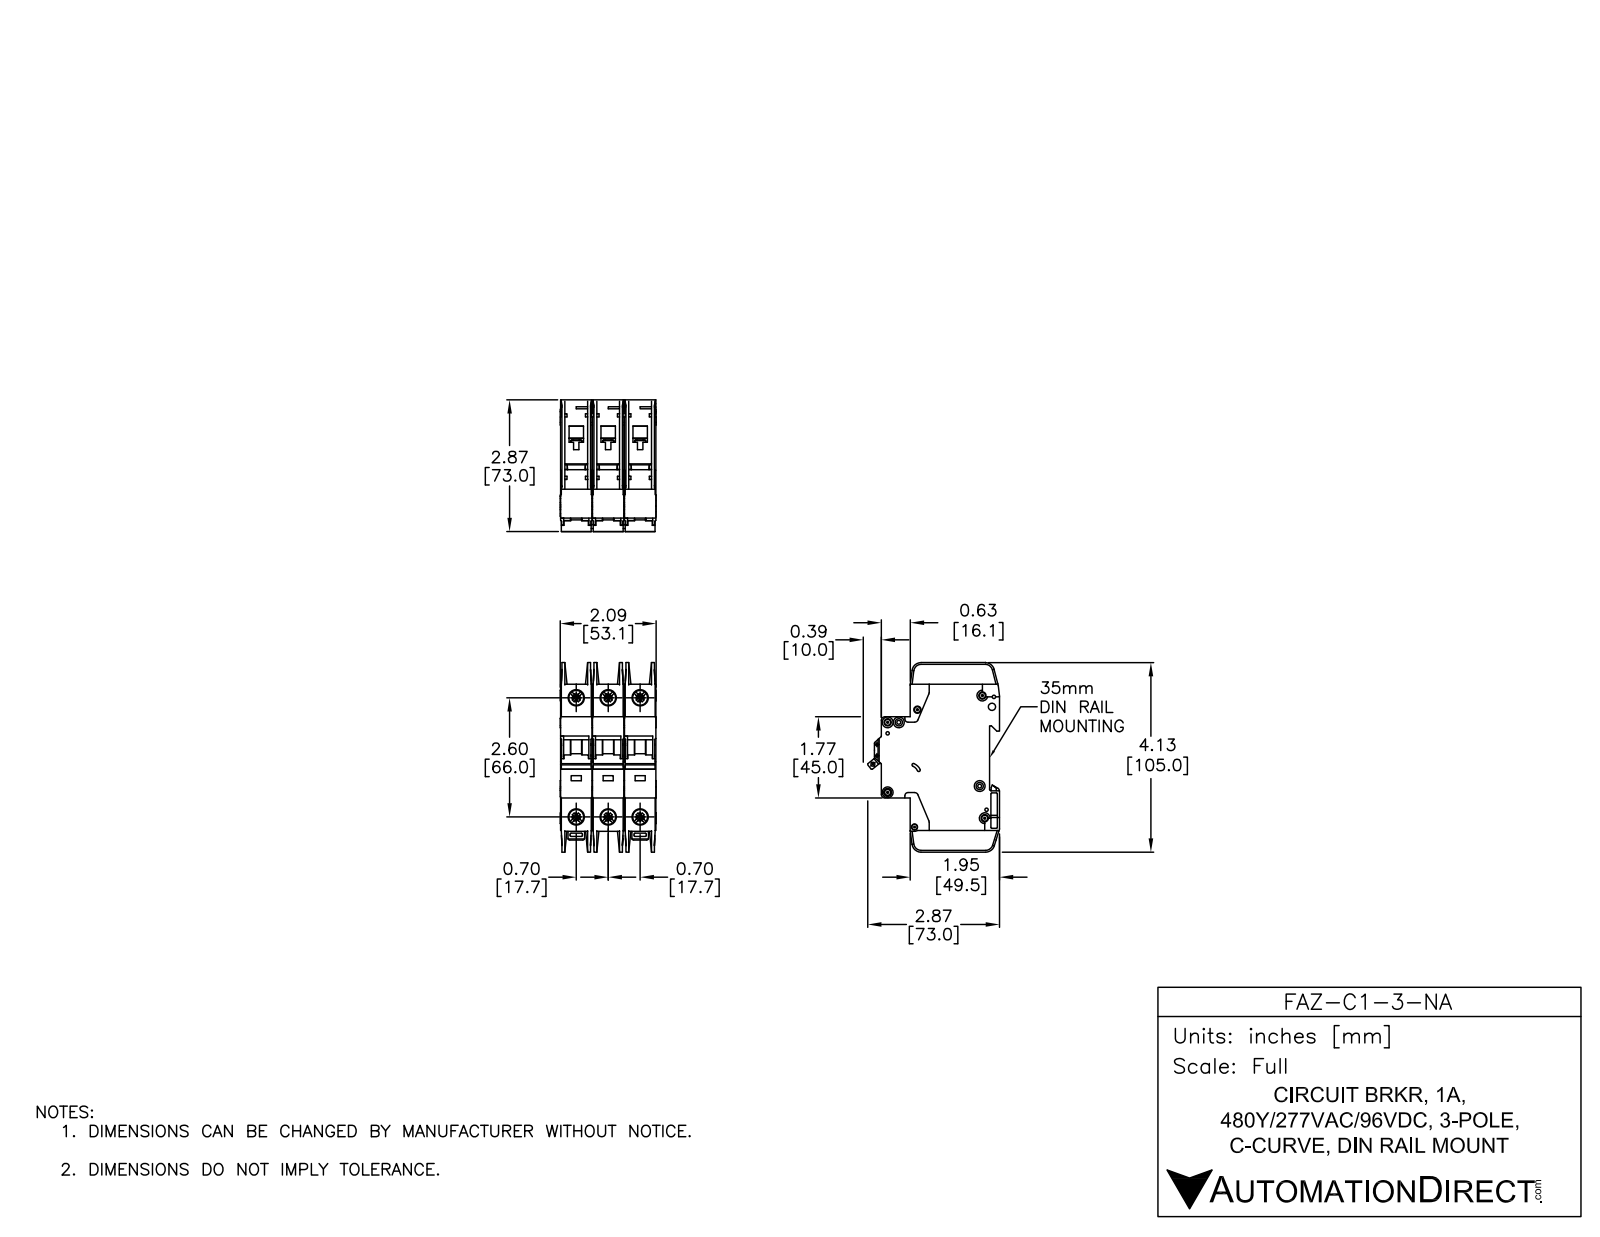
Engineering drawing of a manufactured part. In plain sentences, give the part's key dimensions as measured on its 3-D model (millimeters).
The part is named "FAZ-C1-3-NA". Its 3-D file was written by "SolidWorks 2014 (AUTOMOTIVE_DESIGN)". It is 9 solids with 2352 faces: 1227 planar, 789 cylindrical and 336 other. Overall it measures 105 by 73.04 by 53.1 millimeters. Its volume is 233 085 cubic millimeters and its surface area 74 219 square millimeters. Round holes: 7 of diameter 3.6, 6 of diameter 7.15, 6 of diameter 8.2, 2 of diameter 1.09, 2 of diameter 1.5, 2 of diameter 4, 1 of diameter 1.9, 1 of diameter 2.15, 1 of diameter 2.2, 1 of diameter 2.55, 1 of diameter 3.3, 1 of diameter 3.4. Round bosses or shafts: 7 of diameter 6, 3 of diameter 2.5. Partial cylindrical surfaces (rounded edges, fillets, slot ends): 65 of radius 0.25, 30 of radius 0.5, 26 of radius 1, 14 of radius 2, 5 of radius 1.8, 5 of radius 5, 4 of radius 4, 2 of radius 0.2. The main face-to-face distances are 17.7, 35.4, 17.5, 35.2, 0.7, 15.05, 2.45, 1.75, 15.75, 13.3. The hole center spacings are 17.7, 68.33, 66, 6.2, 35.4, 74.89, 5.19, 6.1.
